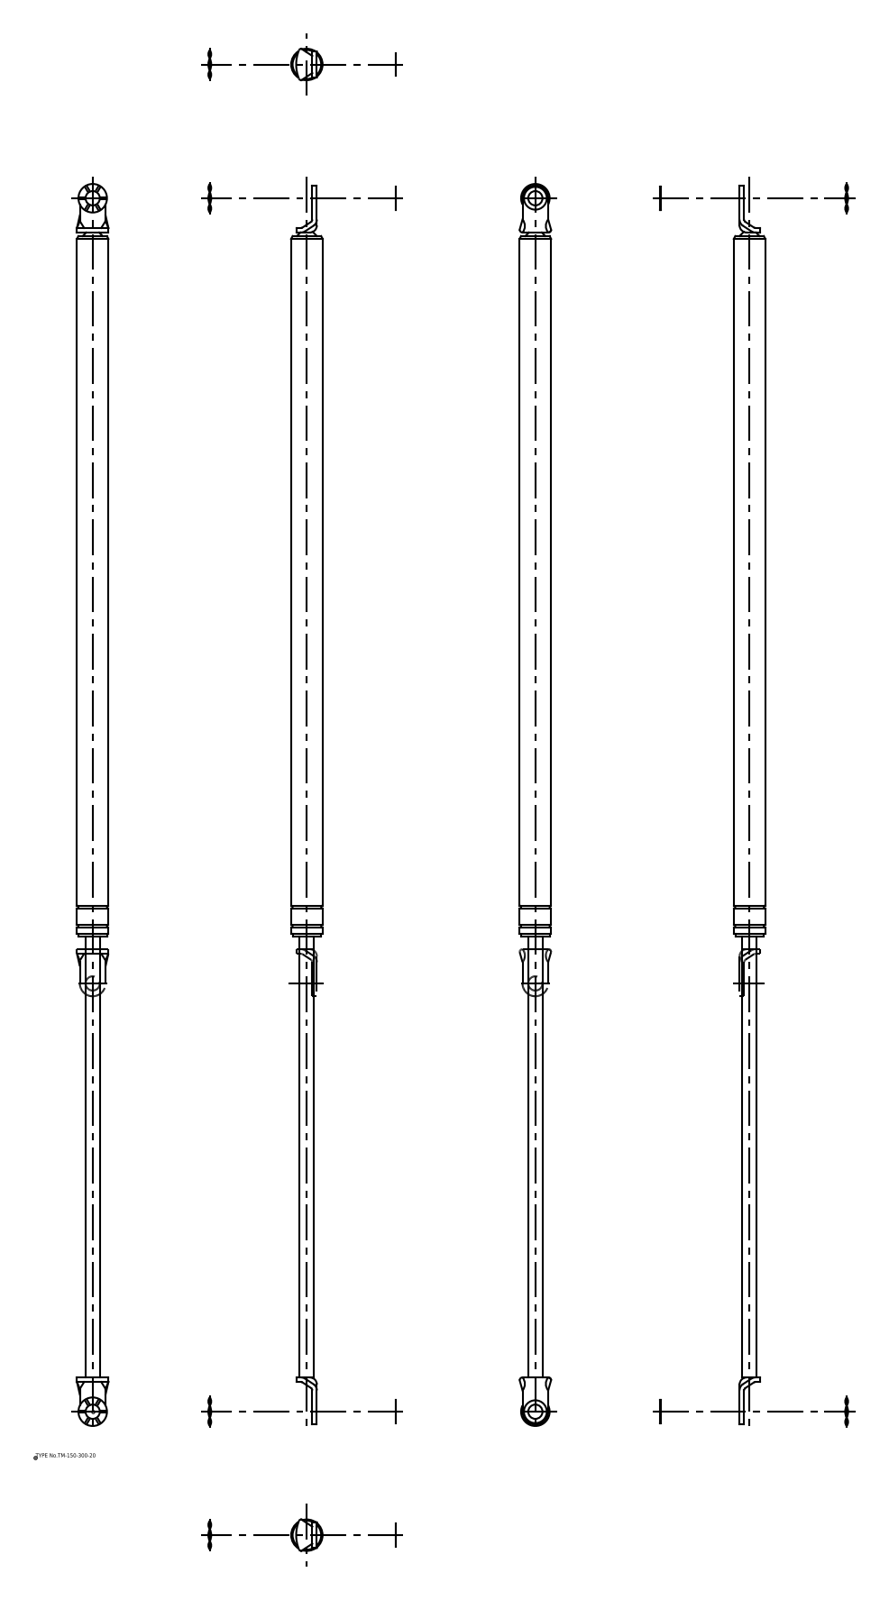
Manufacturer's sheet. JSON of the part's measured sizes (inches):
{"part_name": "ウェーブワッシャー; ワッシャー; 本体; 本体_div", "step_written_by": "spGate 16.7.1 (AUTOMOTIVE_DESIGN)", "units": "inches", "bodies": {"solids": 6, "faces": 94, "planar": 42, "cylindrical": 44, "other": 8}, "overall_size": [34.252, 0.886, 0.886], "volume_in3": 13.21, "surface_area_in2": 77.67, "round_holes": [[0.394, 2]], "round_bosses_or_shafts": [[0.787, 3], [0.63, 2], [0.886, 1], [0.866, 1], [0.394, 1]], "partial_cylinders_radius": [[0.173, 2], [0.197, 2], [0.354, 2], [1.036, 1]], "face_to_face_distances": [0.126, 0.079, 0.205, 31.701, 0.224, 0.146, 0.02, 19.535, 12.291, 31.827], "hole_center_spacings": [33.465]}
